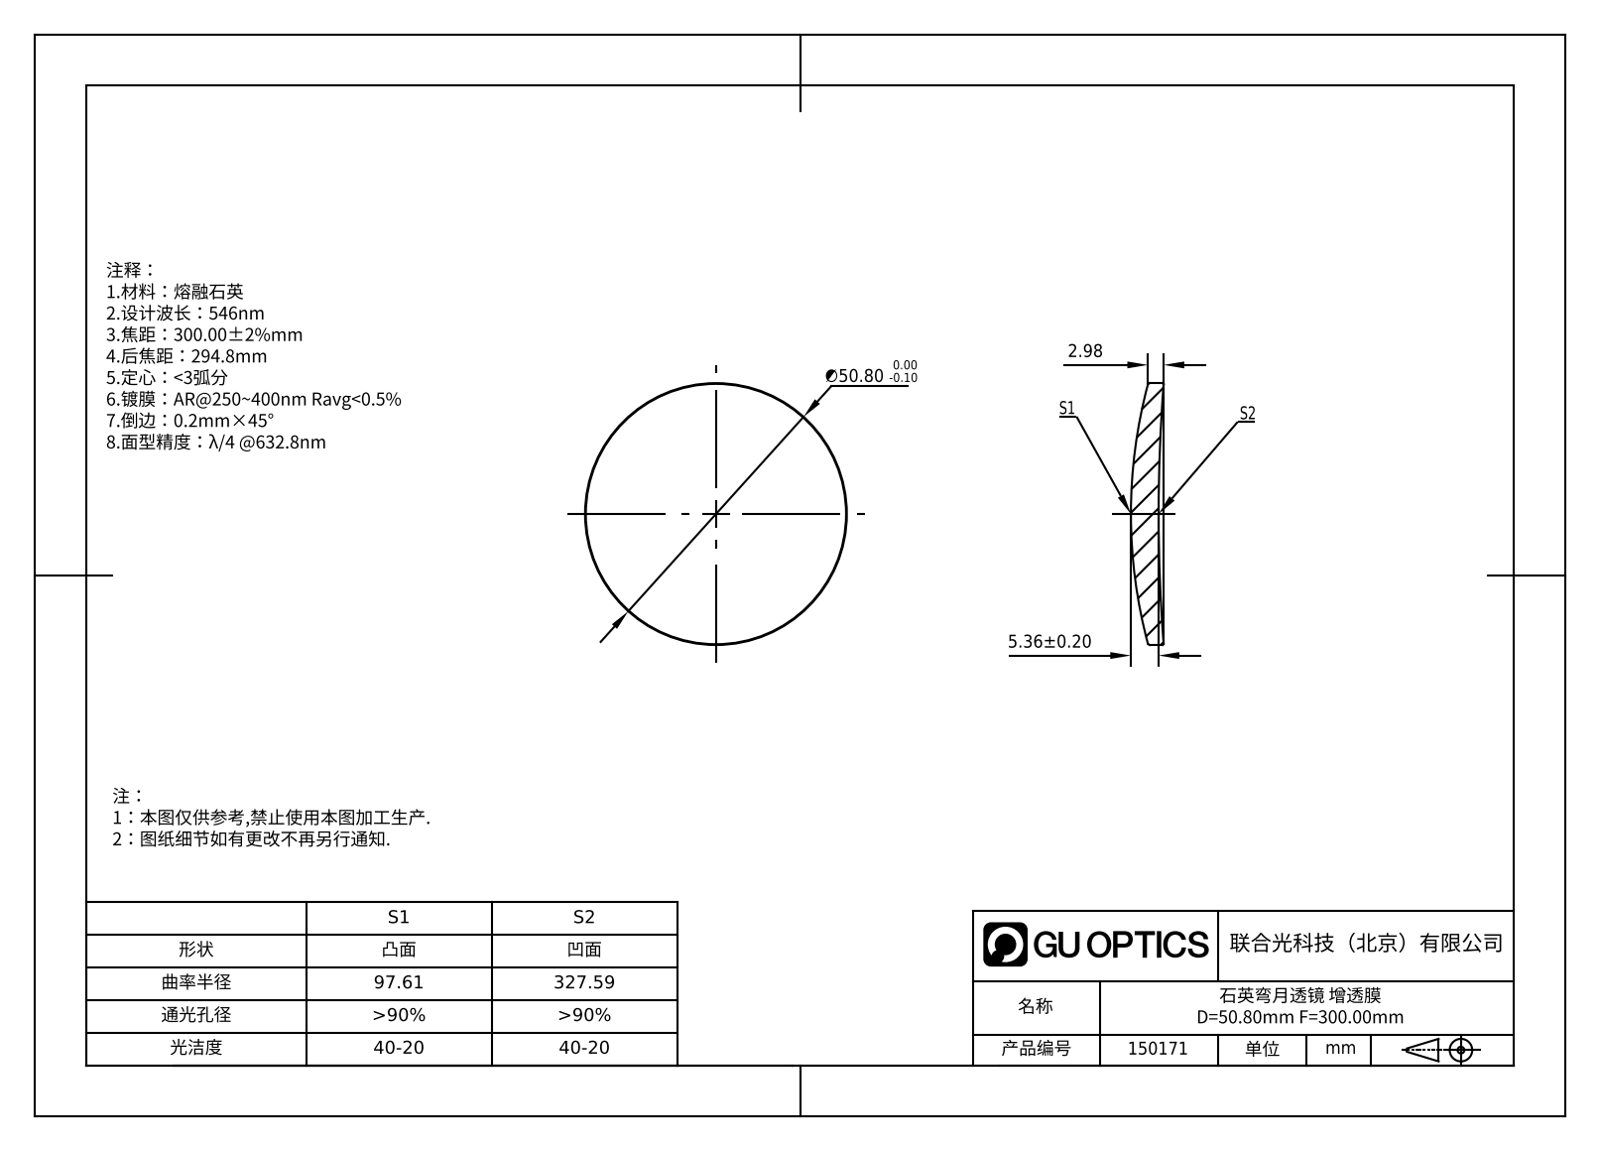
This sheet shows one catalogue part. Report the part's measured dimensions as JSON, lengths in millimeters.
{"part_name": "GLM2-050B-300-UV", "step_written_by": "SolidWorks 2022 (AUTOMOTIVE_DESIGN)", "units": "millimeters", "bodies": {"solids": 1, "faces": 10, "planar": 0, "cylindrical": 2, "other": 8}, "overall_size": [50.8, 50.8, 6.35], "volume_mm3": 8501, "surface_area_mm2": 4536, "round_bosses_or_shafts": [[50.8, 1]]}
